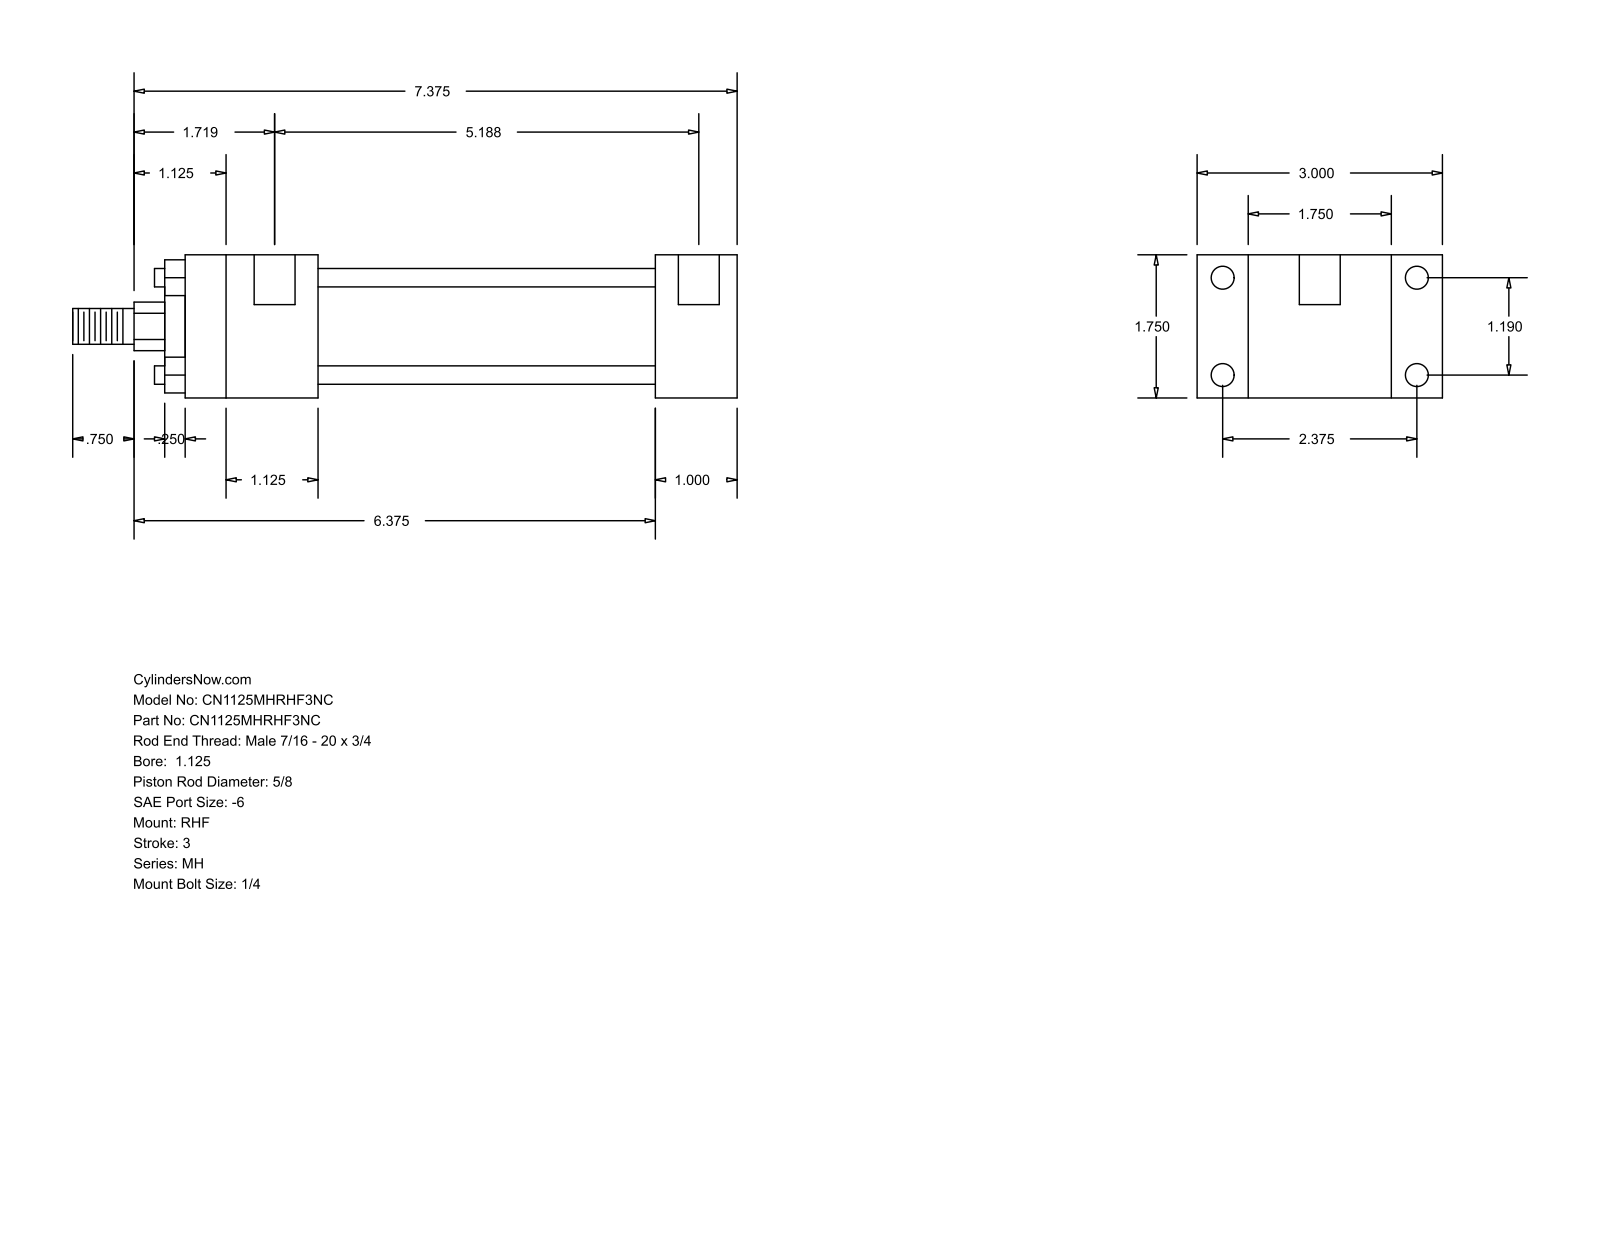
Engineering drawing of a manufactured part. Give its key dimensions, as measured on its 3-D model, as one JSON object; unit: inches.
{"part_name": "MH_RHF__0112_0.625", "step_written_by": "GSSL Pune (CONFIG_CONTROL_DESIGN)", "units": "inches", "bodies": {"solids": 0, "faces": 88, "planar": 60, "cylindrical": 28, "other": 0}, "overall_size": [8.125, 3, 1.75], "round_holes": [[0.219, 4], [0.281, 4], [0.5, 2]], "round_bosses_or_shafts": [[0.225, 4], [1.375, 1], [1.125, 1], [0.625, 1], [0.437, 1]], "partial_cylinders_radius": [[0.297, 1]], "face_to_face_distances": [1.75, 0.625, 2.375, 1, 3, 4.125, 5.125, 1.625, 5.75, 6.75], "hole_center_spacings": [1.19, 2.375, 2.656, 5.063, 0.125, 5.187]}
